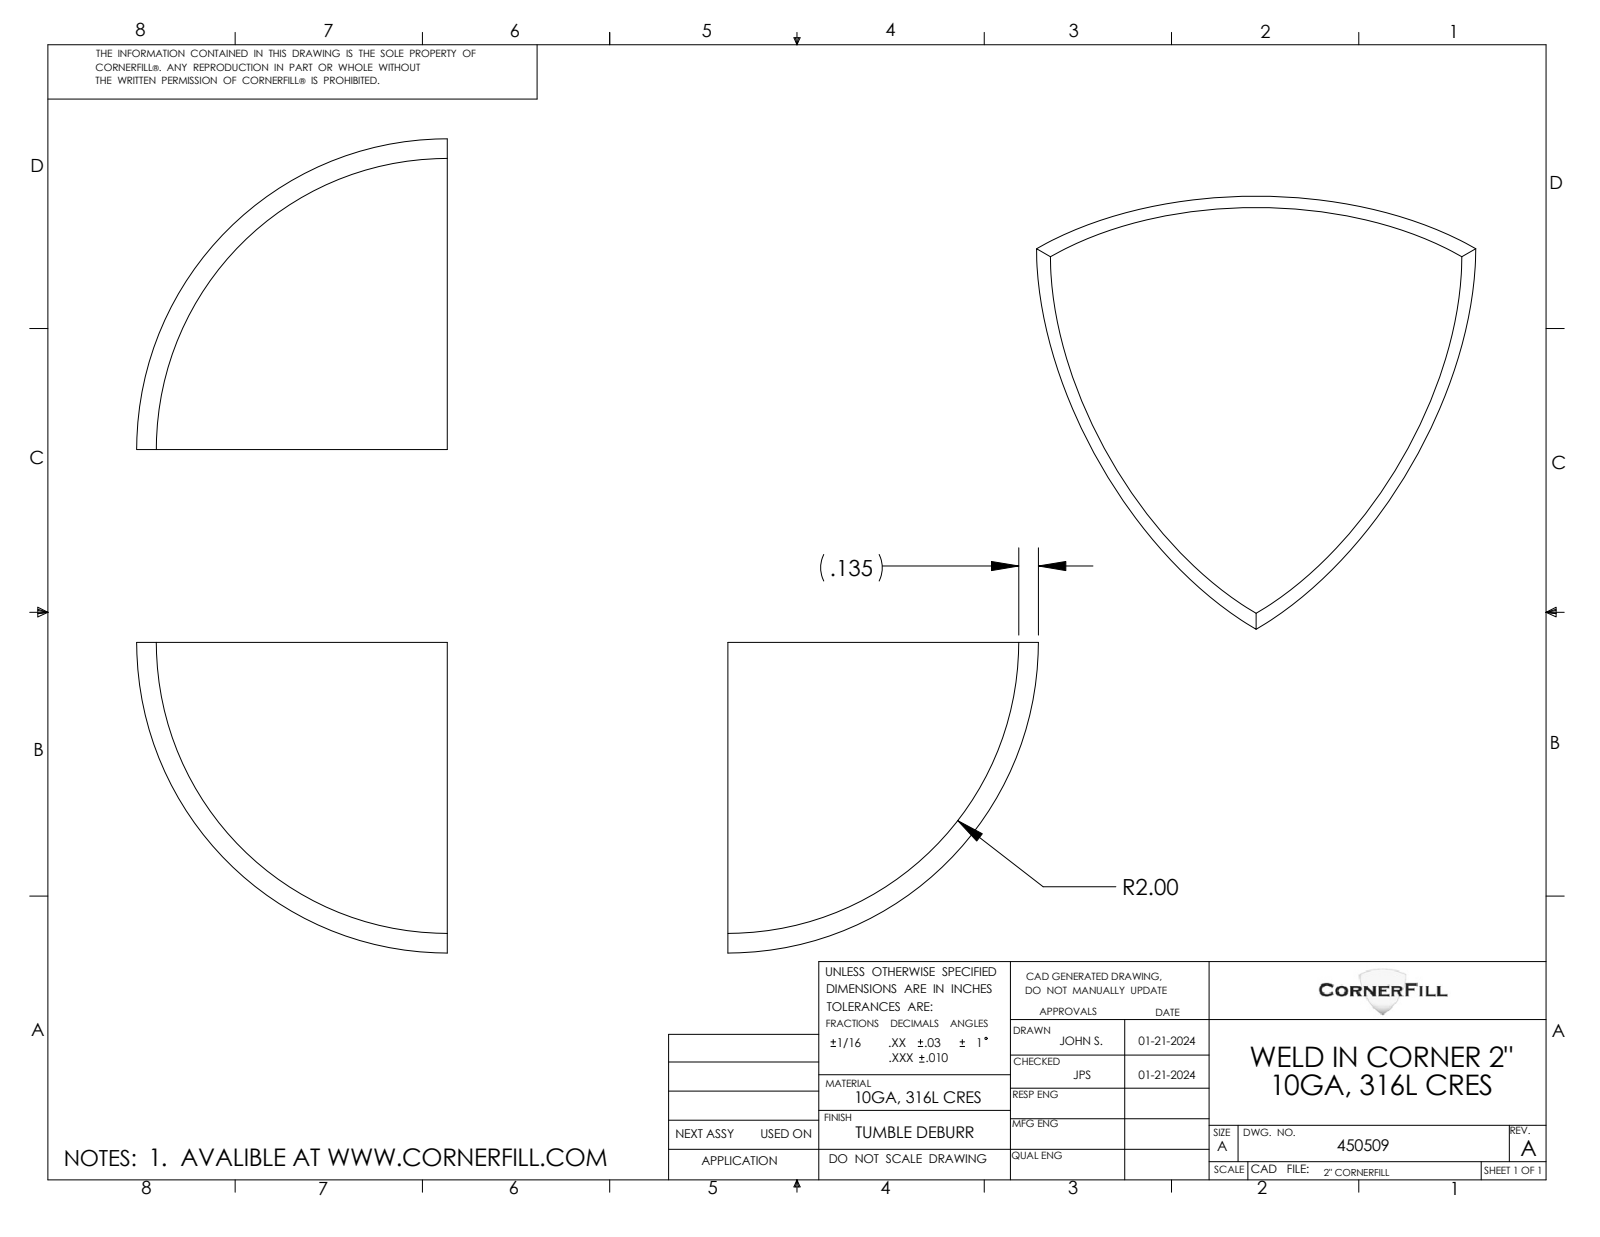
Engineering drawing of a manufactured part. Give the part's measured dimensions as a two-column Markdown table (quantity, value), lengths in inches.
| quantity | value |
| --- | --- |
| part name | 450509 |
| STEP written by | SolidWorks 2021 (CONFIG_CONTROL_DESIGN) |
| units | inches |
| bodies | 1 solid, 5 faces (3 planar, 0 cylindrical, 2 other) |
| overall size | 3.019 × 2.135 × 2.135 |
| volume | 0.907 in³ |
| surface area | 14.76 in² |
